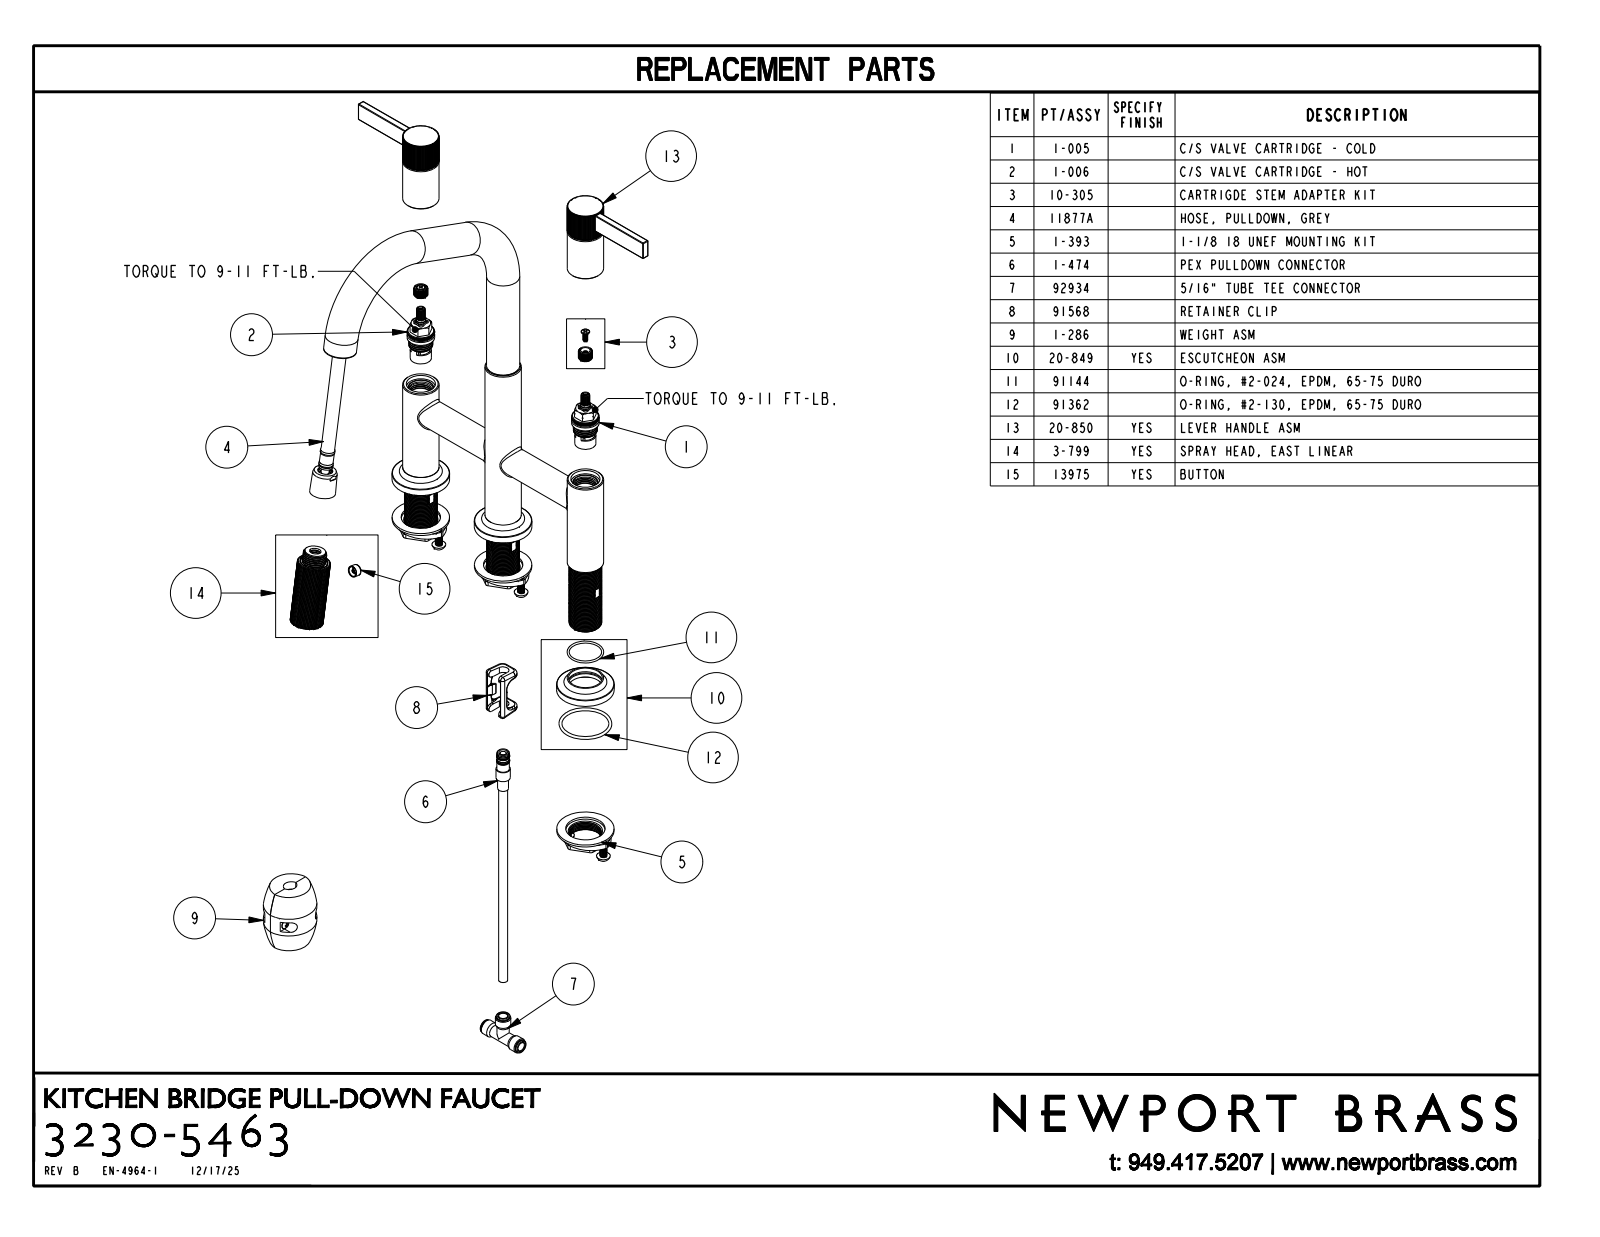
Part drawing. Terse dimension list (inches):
name: 13656; 1-471_ASM; 1-472_ASM; 1-473_ASM (+8 more)
written by: CREO PARAMETRIC BY PTC INC, 2023134 (CONFIG_CONTROL_DESIGN)
unit: in
bodies: 22 solids, 2350 faces (1477 planar, 655 cylindrical, 218 other)
size: 14.415 × 13.85 × 9.83
volume: 46.7 in³; area: 264.3 in²
holes: 48× ⌀0.039, 3× ⌀1.15, 3× ⌀1.255, 2× ⌀0.383, 2× ⌀0.535, 2× ⌀0.598, 2× ⌀0.638, 2× ⌀1, 1× ⌀0.084, 1× ⌀0.345, 1× ⌀0.394, 1× ⌀0.472
bosses: 18× ⌀0.102, 18× ⌀0.079, 3× ⌀1.98, 3× ⌀1.25, 3× ⌀1.14, 2× ⌀0.551, 2× ⌀0.51, 2× ⌀0.506
rounds: 12× R0.02, 6× R0.03, 6× R0.125, 3× R0.01, 2× R0.07, 2× R0.098, 2× R0.225, 1× R0.475
face distances: 0.5, 0.265, 0.15, 0.35, 0.085, 0.235, 0.315, 0.58, 0.23, 0.08
hole spacings: 0.364, 0.487, 0.724, 0.365, 0.541, 0.631, 0.665, 0.364
